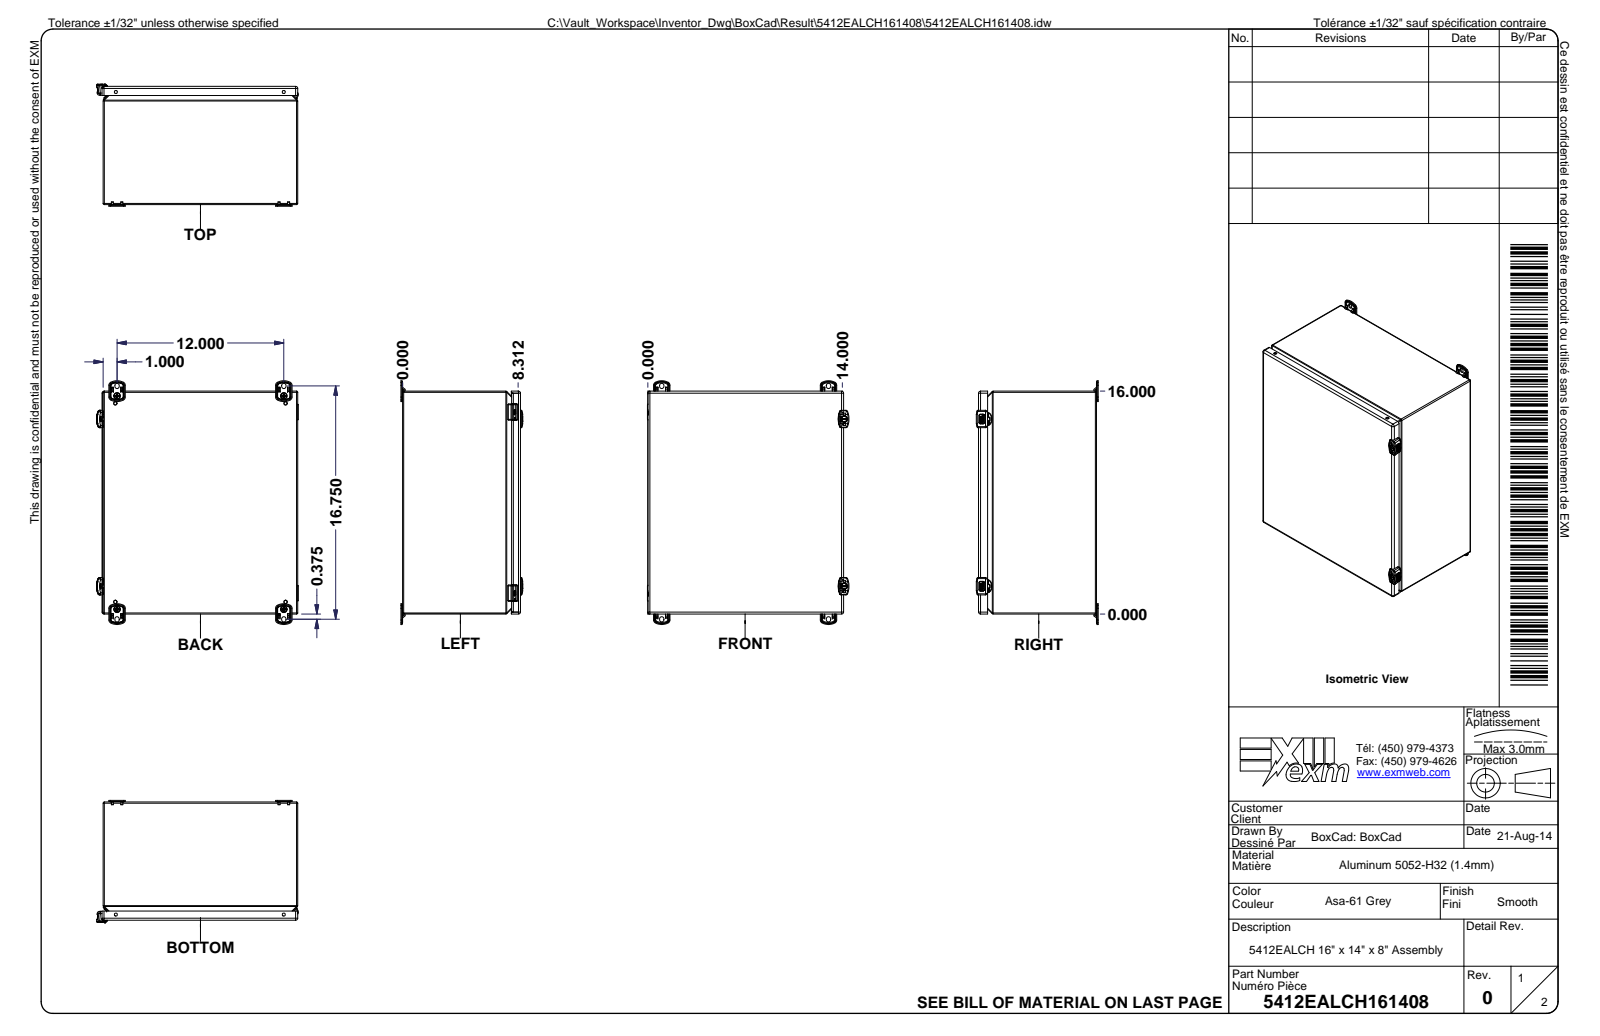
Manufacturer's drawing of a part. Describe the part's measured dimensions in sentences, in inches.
The part is named "5412EALCH161408; 5412EALCH161408B; 5412EALCH161408B-P; STK-A-70469-1 (+8 more)". Its 3-D file was written by "Autodesk Inventor 2020 (AUTOMOTIVE_DESIGN)". It is 59 solids with 8409 faces: 3583 planar, 2002 cylindrical and 2824 other. Overall it measures 17.496 by 14.503 by 8.76 inches. Its volume is 70.71 cubic inches and its surface area 2 522 square inches. Round holes: 4 of diameter 0.165, 4 of diameter 0.173, 4 of diameter 0.197, 4 of diameter 0.197, 4 of diameter 0.236, 4 of diameter 0.236, 4 of diameter 0.32, 2 of diameter 0.03, 2 of diameter 0.175, 2 of diameter 0.201, 2 of diameter 0.24, 2 of diameter 0.339. Round bosses or shafts: 8 of diameter 0.232, 4 of diameter 0.5, 4 of diameter 0.3, 4 of diameter 0.236, 4 of diameter 0.193, 3 of diameter 0.197, 2 of diameter 0.412, 2 of diameter 0.394. Partial cylindrical surfaces (rounded edges, fillets, slot ends): 258 of radius 0.02, 209 of radius 0.01, 92 of radius 0.039, 64 of radius 0.004, 60 of radius 0.008, 57 of radius 0.059, 35 of radius 0.031, 33 of radius 0.005. The main face-to-face distances are 0.053, 0.053, 13.947, 8.433, 8.38, 15.947, 8.486, 8.433, 0.236, 0.304. The hole center spacings are 19.118, 0.546, 12.137, 14.781, 12, 12.25, 12.25, 14.25.
